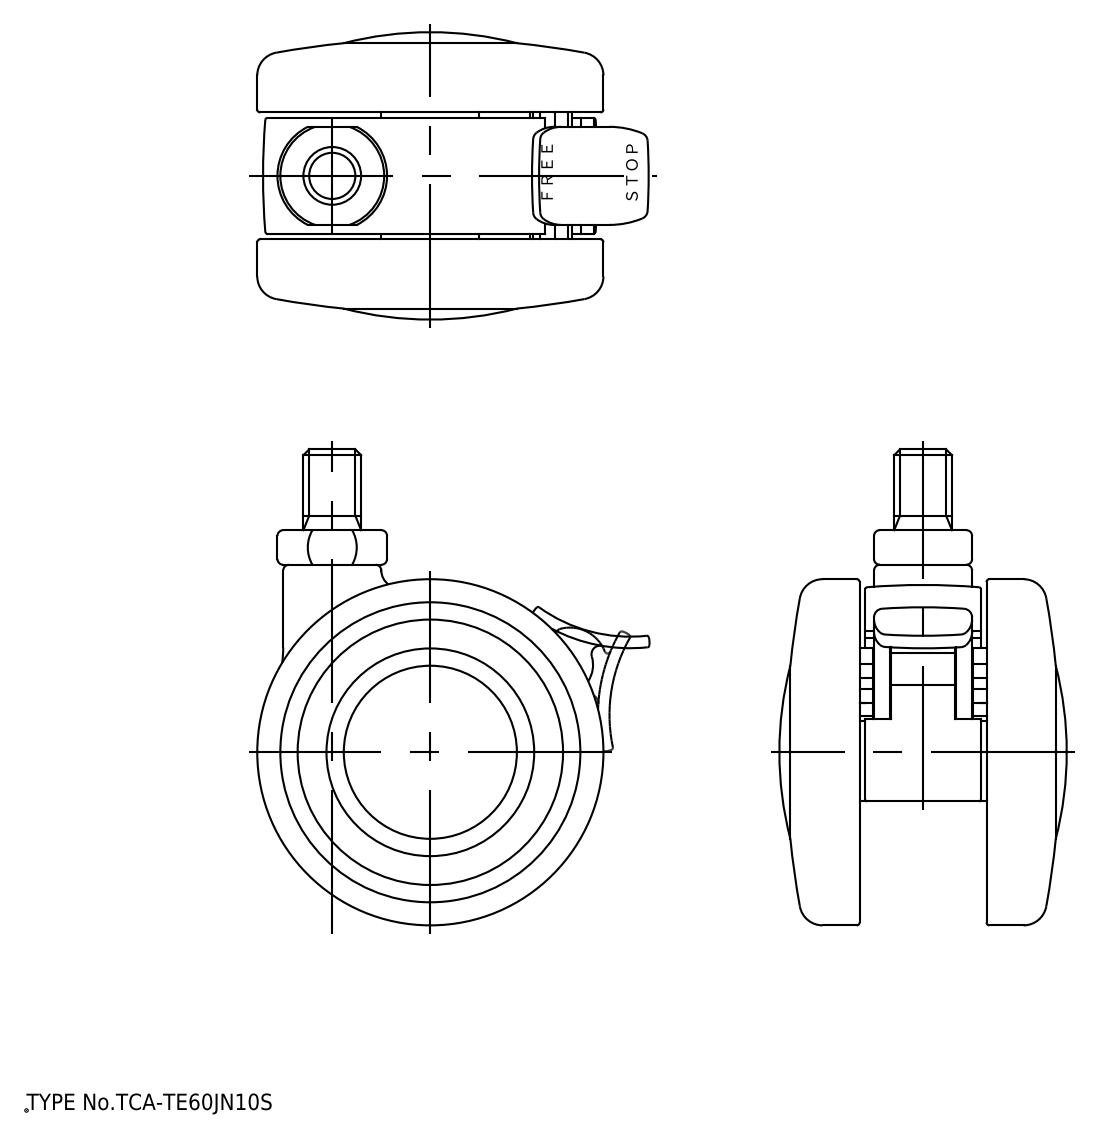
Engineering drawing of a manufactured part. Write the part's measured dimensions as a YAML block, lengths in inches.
part_name: "TCA-TE60J_Wheel; TCA-TE60JN10_Shaft; TCA-TE60JS_Body; TCA-TE60JS_Stopper"
step_written_by: "spGate 18.9.1 (****-****-****-****) (AUTOMOTIVE_DESIGN)"
units: inches
bodies: {solids: 5, faces: 260, planar: 67, cylindrical: 114, other: 79}
overall_size: [3.248, 2.711, 1.935]
volume: 5.205
surface_area: 52.41
round_holes:
  - {diameter: 0.138, count: 1}
  - {diameter: 0.315, count: 1}
  - {diameter: 0.366, count: 1}
  - {diameter: 0.421, count: 1}
  - {diameter: 0.787, count: 1}
  - {diameter: 1.189, count: 1}
  - {diameter: 1.772, count: 1}
round_bosses_or_shafts:
  - {diameter: 2.362, count: 1}
  - {diameter: 1.417, count: 1}
  - {diameter: 1.177, count: 1}
  - {diameter: 0.709, count: 1}
  - {diameter: 0.669, count: 1}
  - {diameter: 0.413, count: 1}
  - {diameter: 0.394, count: 1}
  - {diameter: 0.256, count: 1}
partial_cylinders:
  - {radius: 0.012, count: 6}
  - {radius: 0.039, count: 5}
  - {radius: 0.059, count: 5}
  - {radius: 0.079, count: 5}
  - {radius: 0.591, count: 2}
  - {radius: 1.043, count: 2}
  - {radius: 1.142, count: 2}
  - {radius: 3.926, count: 2}
face_to_face_distances: [0.197, 0.433, 0.079, 1.024, 0.276, 1.201, 0.748, 0.945, 0.827, 1.122]
hole_center_spacings: [1.083]
